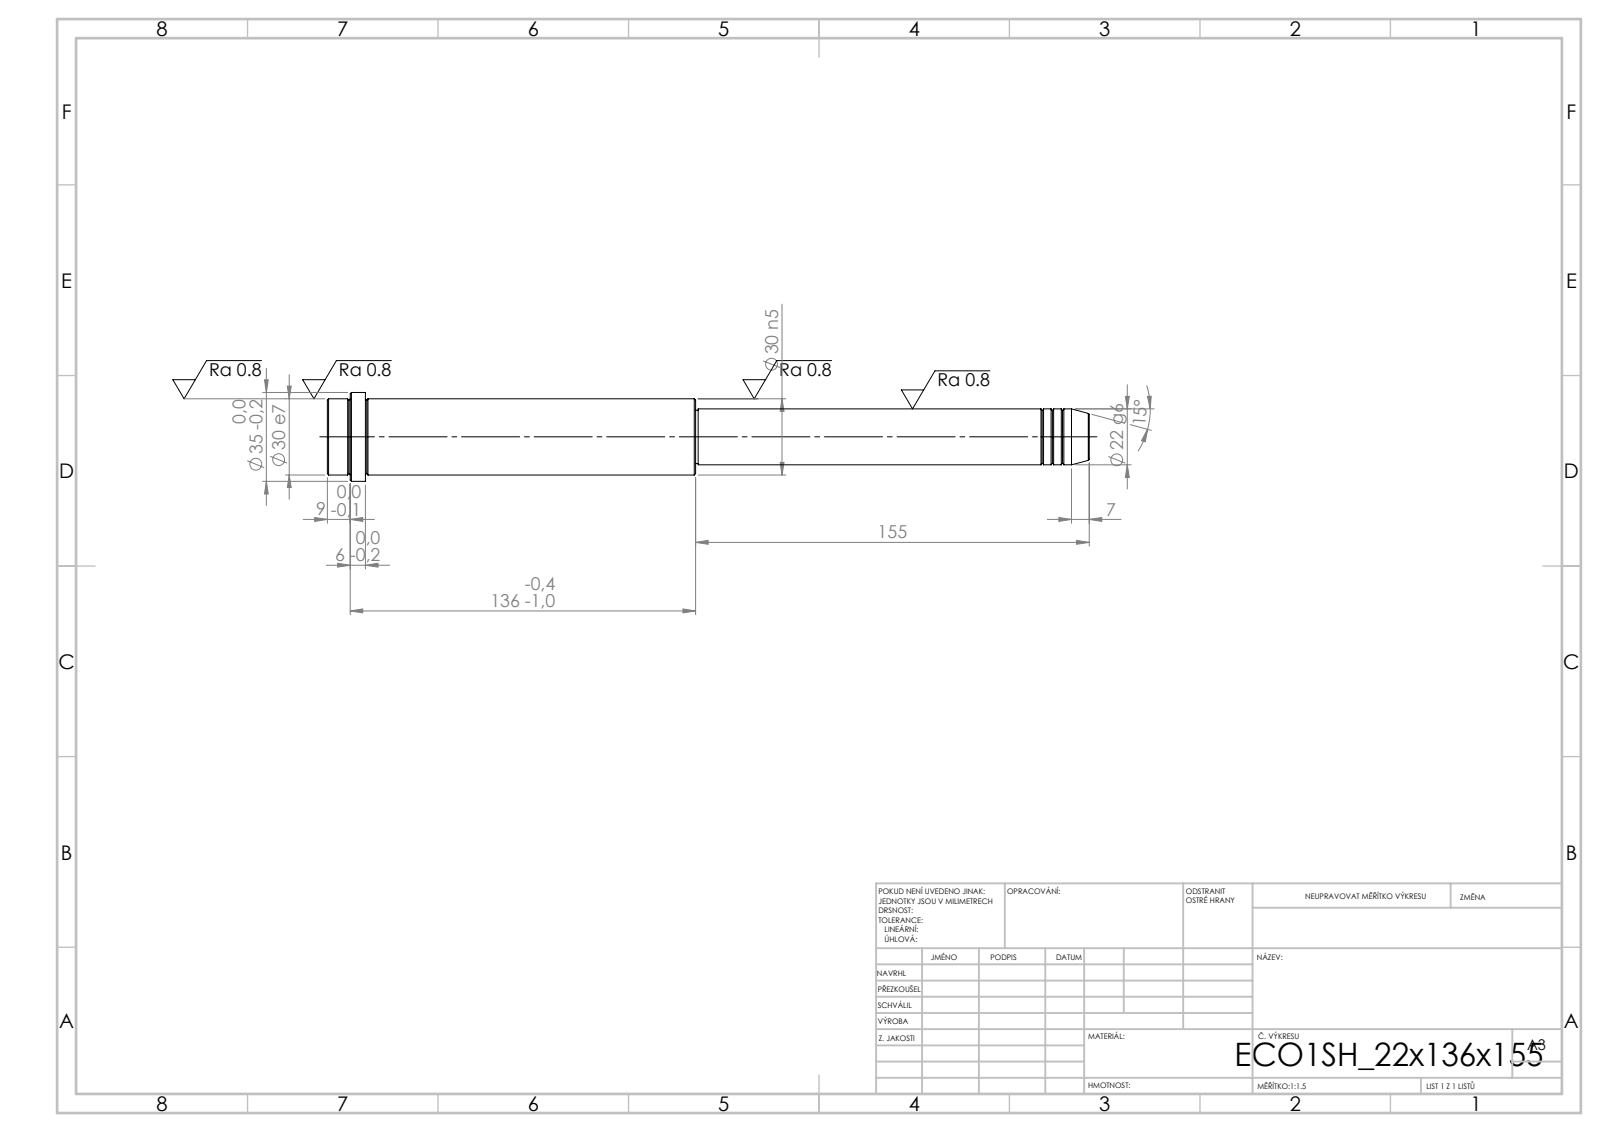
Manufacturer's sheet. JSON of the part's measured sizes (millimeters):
{"step_written_by": "SolidWorks 2019 (CONFIG_CONTROL_DESIGN)", "units": "millimeters", "bodies": {"solids": 1, "faces": 52, "planar": 6, "cylindrical": 16, "other": 30}, "overall_size": [300, 35, 35], "volume_mm3": 162294, "surface_area_mm2": 26433, "round_bosses_or_shafts": [[35, 1], [30, 1], [22, 1], [21, 1]], "face_to_face_distances": [145, 130, 15, 155, 285, 300, 291, 136, 6, 9]}
